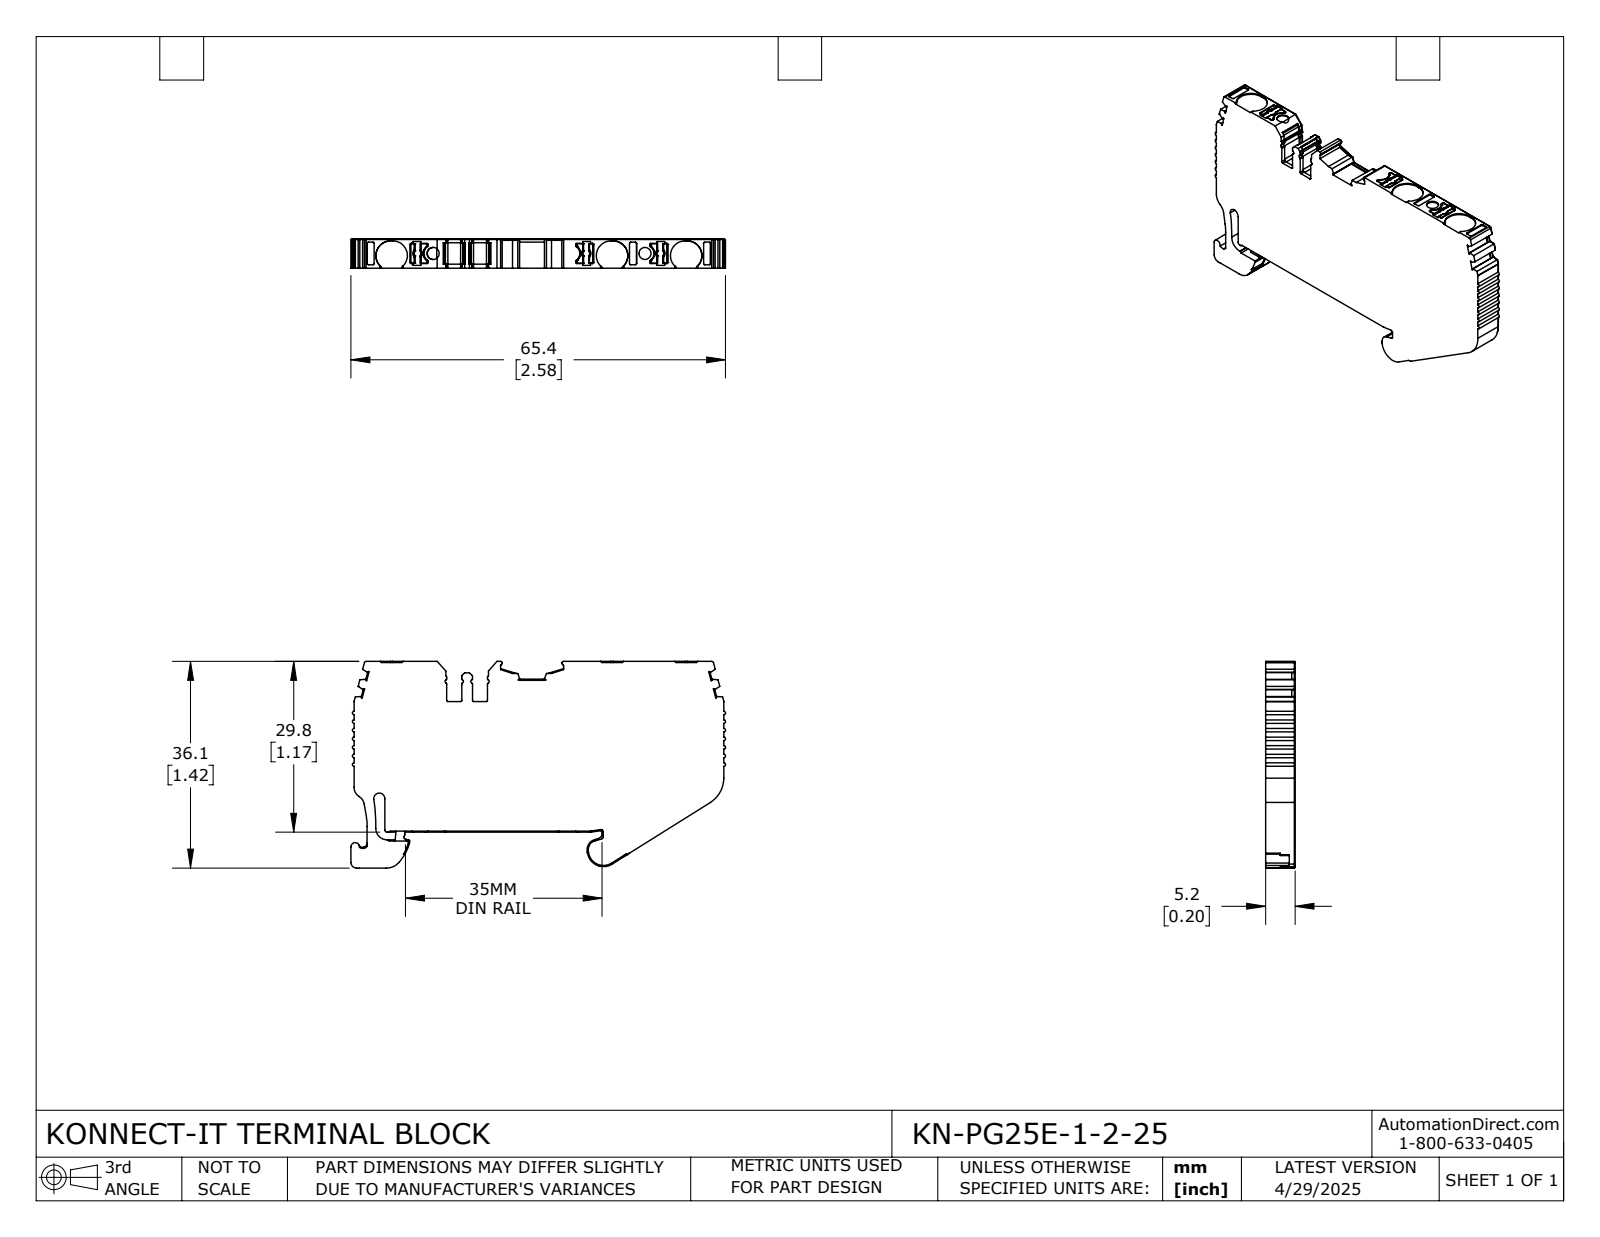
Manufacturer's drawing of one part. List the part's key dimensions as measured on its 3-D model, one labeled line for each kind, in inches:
Part name (STEP PRODUCT): KN-PG25E-1-2-25
STEP written by: SolidWorks 2024 (CONFIG_CONTROL_DESIGN)
Units: inches
Bodies: 1 solid, 708 faces (373 planar, 282 cylindrical, 53 other)
Overall size (bounding box): 2.576 × 1.42 × 0.203
Volume: 0.582 in³ · Surface area: 8.04 in²
Round holes (diameter × count): ⌀0.083 ×2
Partial cylindrical surfaces — rounded edges, fillets, slot ends (radius × count): R0.008 ×65, R0.012 ×42, R0.004 ×19, R0.016 ×17, R0.02 ×16, R0.006 ×12, R0.039 ×8, R0.1 ×6
Main face-to-face distances: 0.203, 1.166, 1.174, 1.158, 2.543, 0.177, 0.197, 0.047, 0.211, 2.331
Hole centre spacings: 1.456
